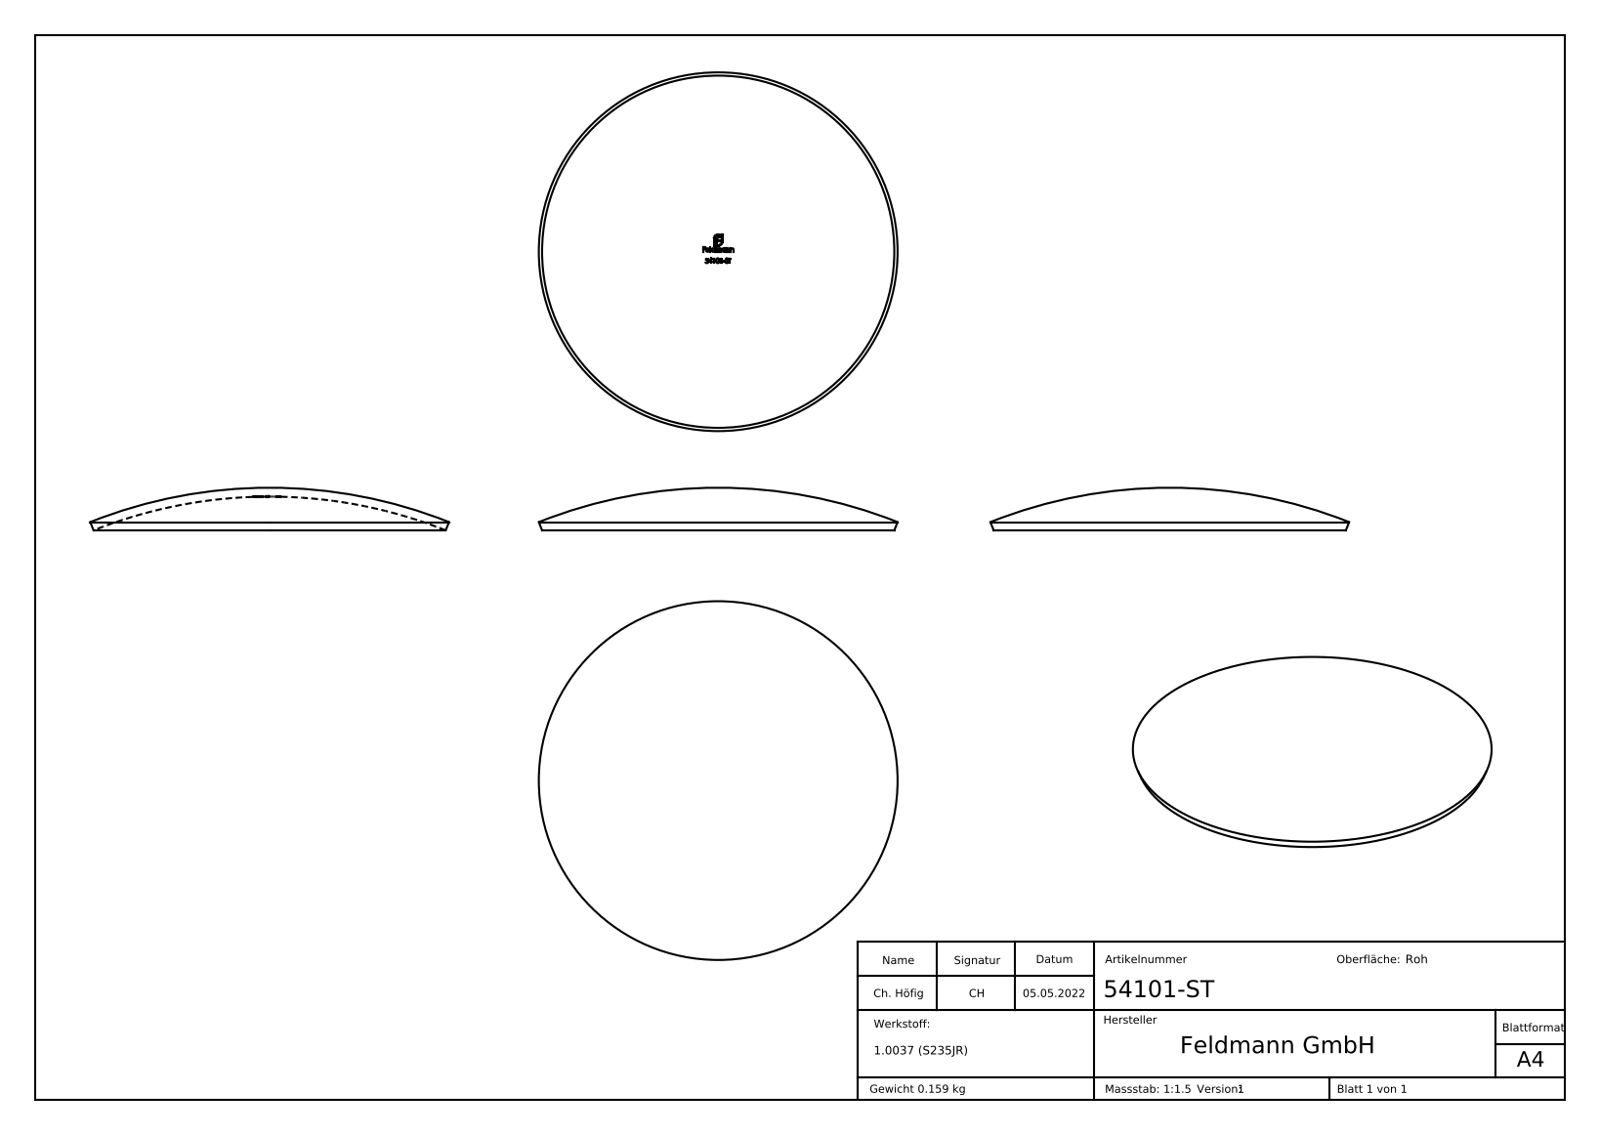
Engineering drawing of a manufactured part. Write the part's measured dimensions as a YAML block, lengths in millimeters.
part_name: "54101-ST"
step_written_by: "SolidWorks 2018 (CONFIG_CONTROL_DESIGN)"
units: millimeters
bodies: {solids: 1, faces: 246, planar: 121, cylindrical: 0, other: 125}
overall_size: [101, 101, 12]
volume: 20387
surface_area: 17108
face_to_face_distances: [4.23, 0.87, 1.14, 1.84, 1.06, 0.68, 3.19, 0.58, 0.34, 2.2]
